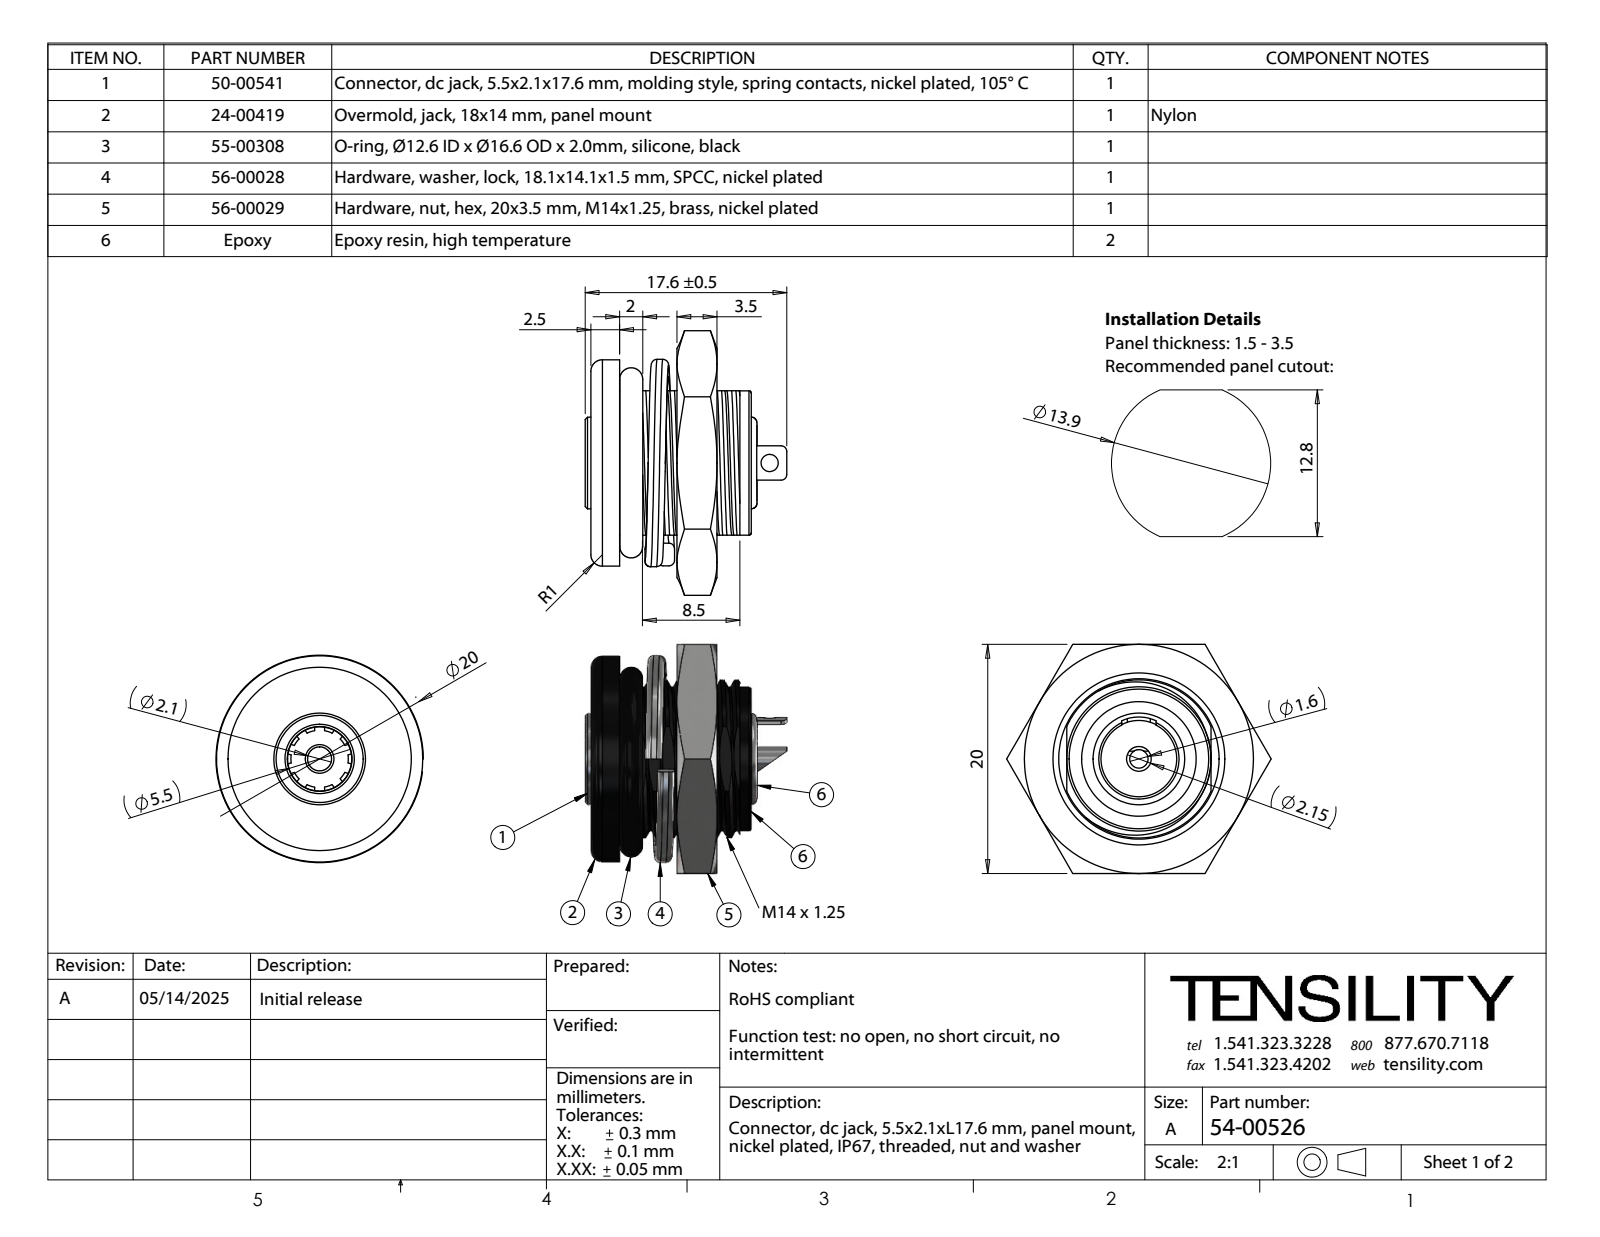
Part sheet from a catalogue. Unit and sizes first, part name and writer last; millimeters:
Units: millimetres
Overall size (bounding box): 23.09 × 20 × 17.6
Round holes (diameter × count): ⌀1.5 ×2, ⌀1.6 ×1, ⌀2.15 ×1, ⌀2.5 ×1, ⌀5.6 ×1, ⌀5.65 ×1, ⌀6.4 ×1, ⌀6.6 ×1, ⌀7.6 ×1, ⌀8 ×1, ⌀10 ×1, ⌀14 ×1
Round bosses / shafts (diameter × count): ⌀18 ×1, ⌀12.6 ×1, ⌀12.59 ×1, ⌀7.3 ×1, ⌀6.2 ×1, ⌀2.1 ×1
Partial cylindrical surfaces — rounded edges, fillets, slot ends (radius × count): R0.5 ×2, R3.35 ×1, R6.9 ×1
Main face-to-face distances: 3.5, 7.51, 11.01, 2.5, 5.01, 8.51, 20, 8.5, 2, 1
Volume: 2 808 mm³ · Surface area: 4 239 mm²
Bodies: 8 solids, 289 faces (101 planar, 81 cylindrical, 107 other)
Part name (STEP PRODUCT): 55-00308; 24-00419; 50-00541 insulator_Insulator; 54-00526 (+6 more)
STEP written by: SolidWorks 2021 (CONFIG_CONTROL_DESIGN)
